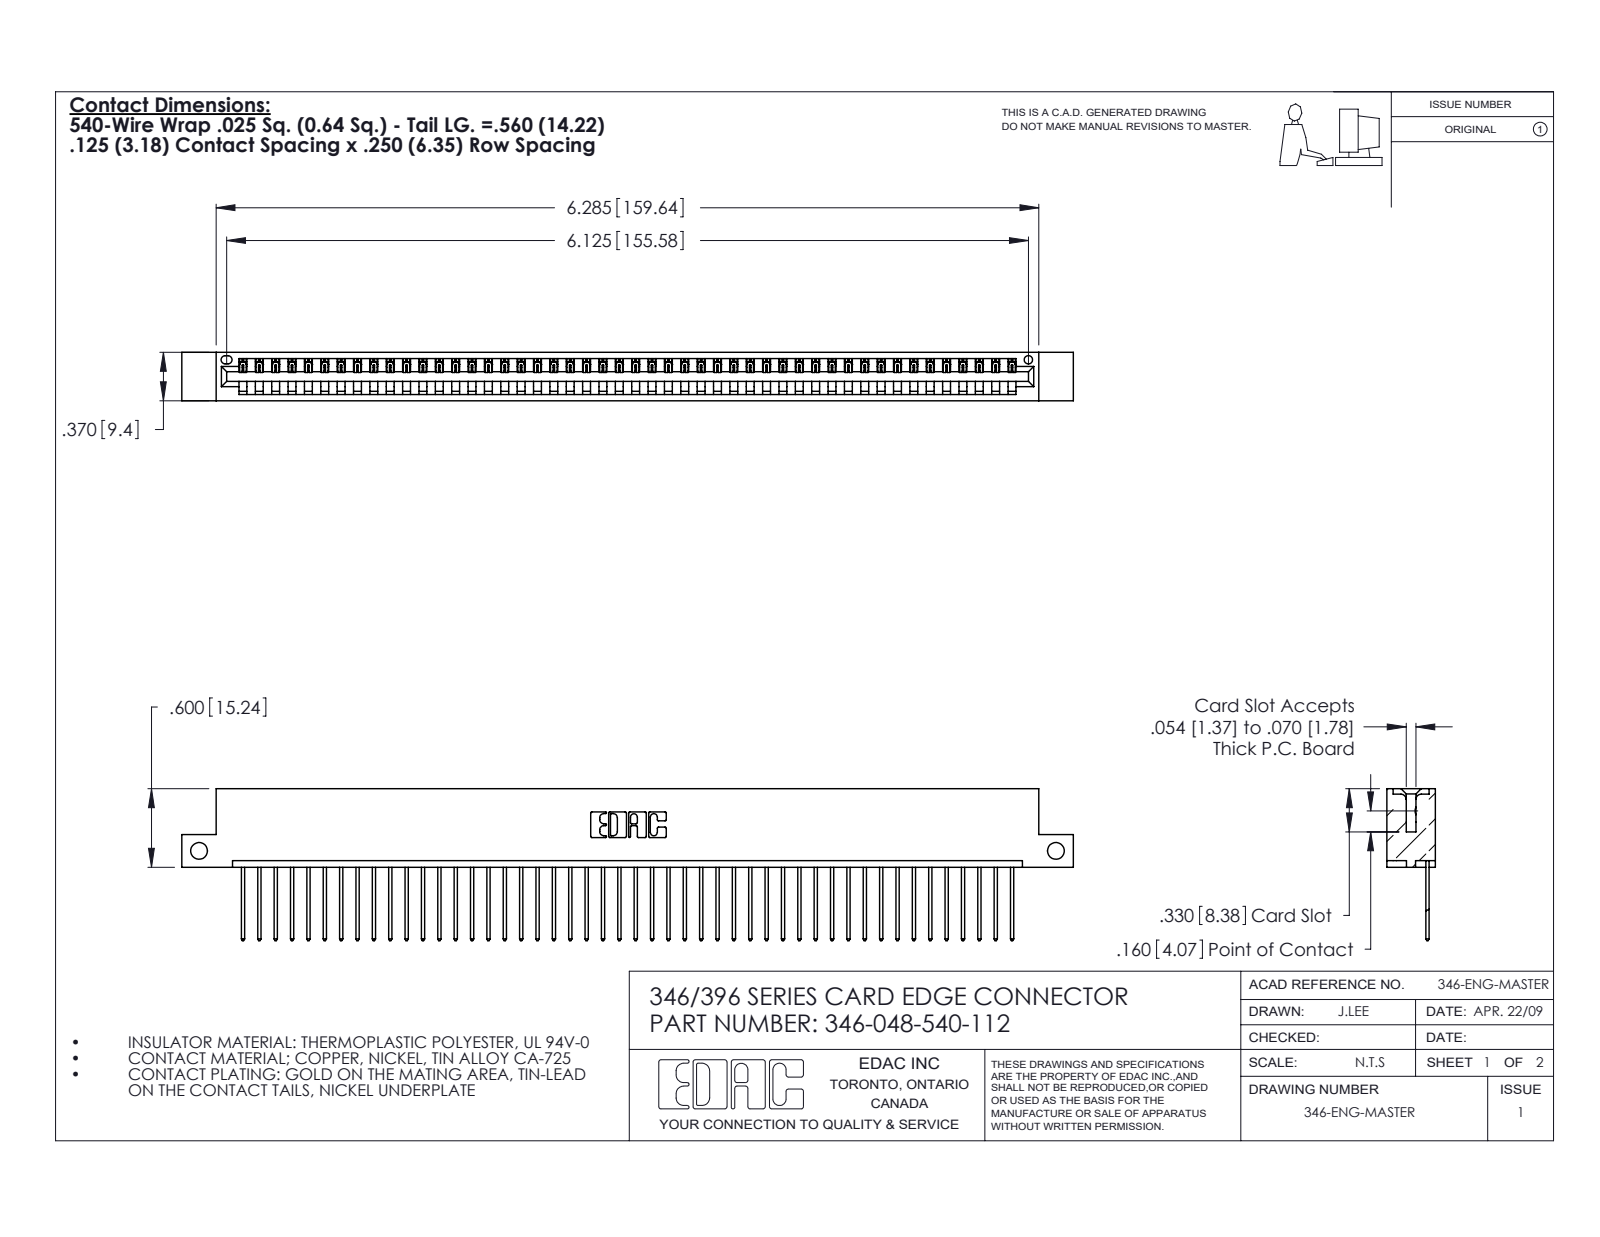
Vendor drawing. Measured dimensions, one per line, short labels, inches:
name: 346 Part_Flush Mounting Lugs - Side Mount; 346-048-540-112; 345-292-001_345-293-140
written by: SolidWorks 2020 (CONFIG_CONTROL_DESIGN)
unit: in
bodies: 49 solids, 2906 faces (1996 planar, 910 cylindrical, 0 other)
size: 6.81 × 1.16 × 0.37
volume: 1.012 in³; area: 32.72 in²
holes: 2× ⌀0.128, 1× ⌀0.064
rounds: 96× R0.006, 96× R0.01, 22× R0.01, 6× R0.007, 6× R0.031, 3× R0.026, 2× R0.031, 2× R0.04
face distances: 0.048, 0.322, 0.37, 0.25, 0.072, 0.298, 0.025, 0.148, 0.222, 0.1
hole spacings: 6.545
